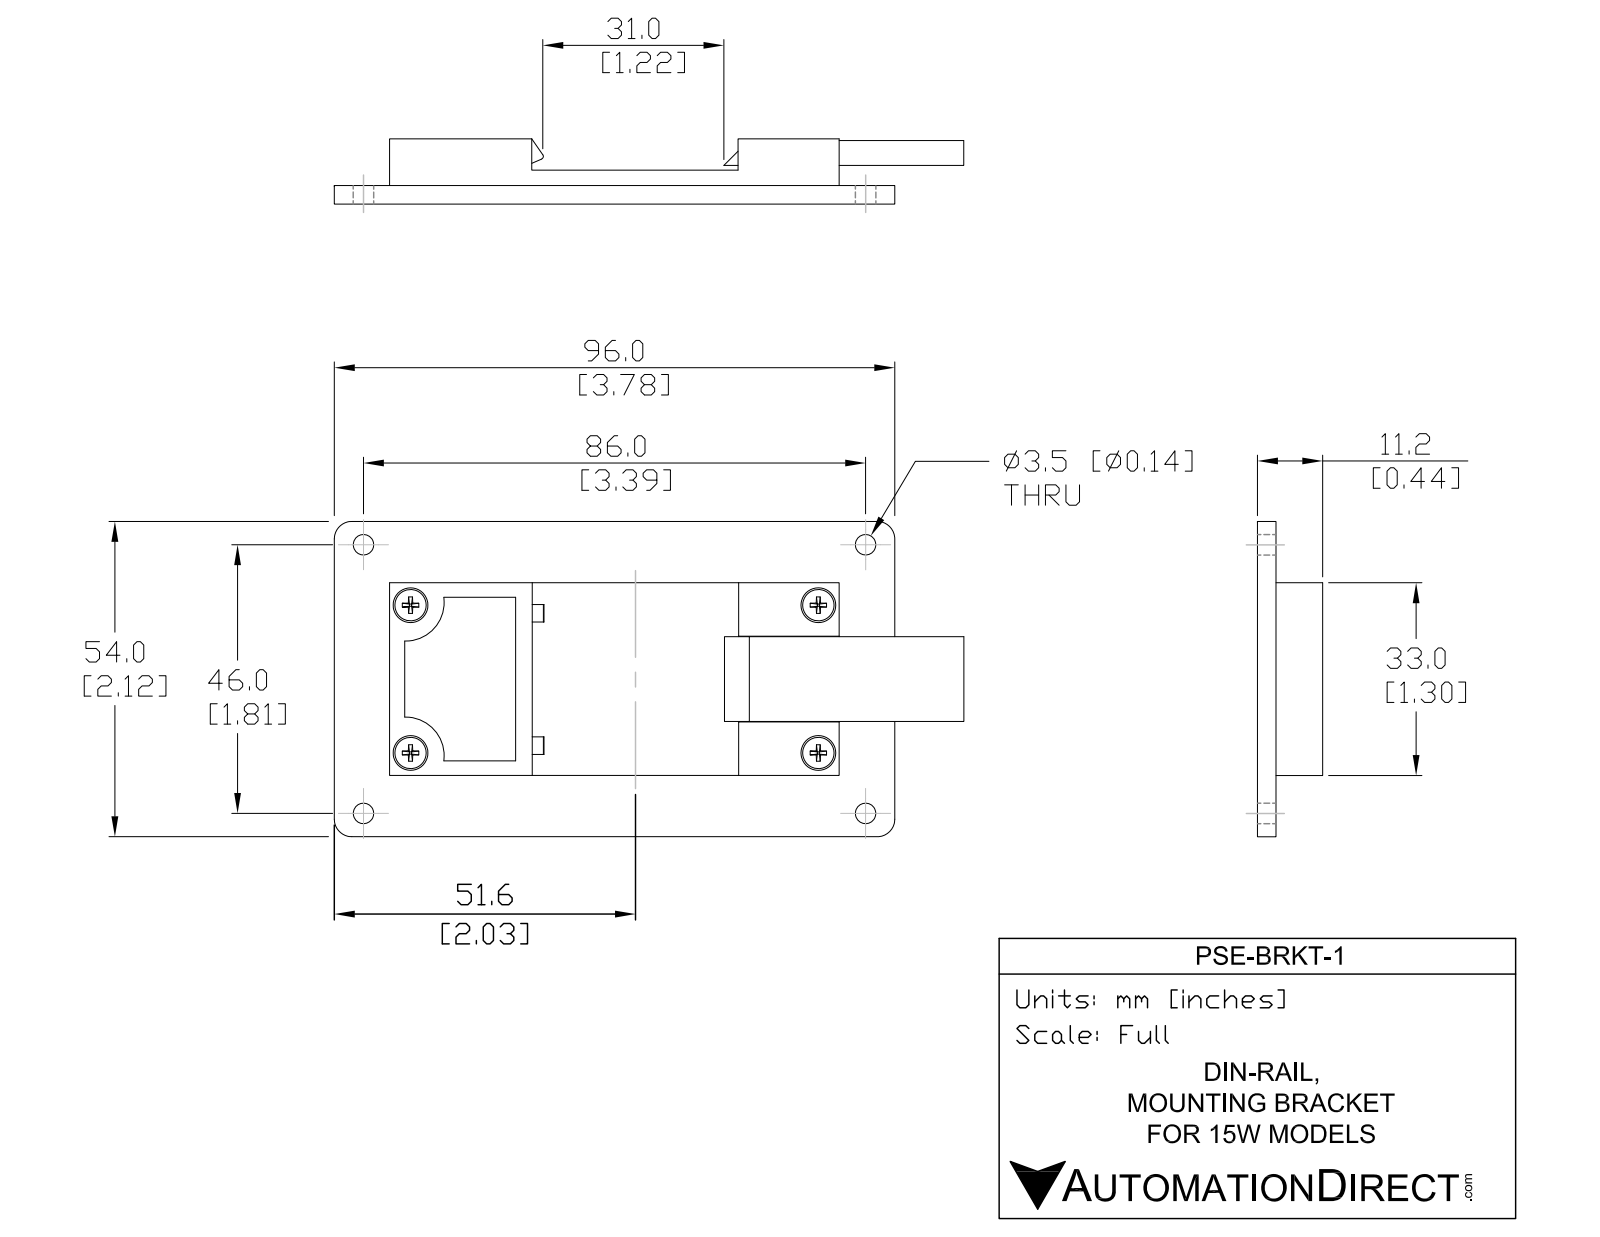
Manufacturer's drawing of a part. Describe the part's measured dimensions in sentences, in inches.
The part is named "PSE-BRKT-1". Its 3-D file was written by "SolidWorks 2011 (CONFIG_CONTROL_DESIGN)". It is 1 solid with 177 faces: 123 planar, 36 cylindrical and 18 other. Overall it measures 4.245 by 2.12 by 0.44 inches. Its volume is 1.729 cubic inches and its surface area 24.2 square inches. Round holes: 4 of diameter 0.14, 4 of diameter 0.23. Round bosses or shafts: 4 of diameter 0.199. Partial cylindrical surfaces (rounded edges, fillets, slot ends): 4 of radius 0.125, 2 of radius 0.26, 1 of radius 0.015. The main face-to-face distances are 0.125, 0.105, 0.23, 0.41, 1.71, 0.2, 0.44, 0.315, 0.21, 0.1. The hole center spacings are 0.54, 0.54, 1, 1.47, 1.47, 1.87, 2.75, 2.926.
